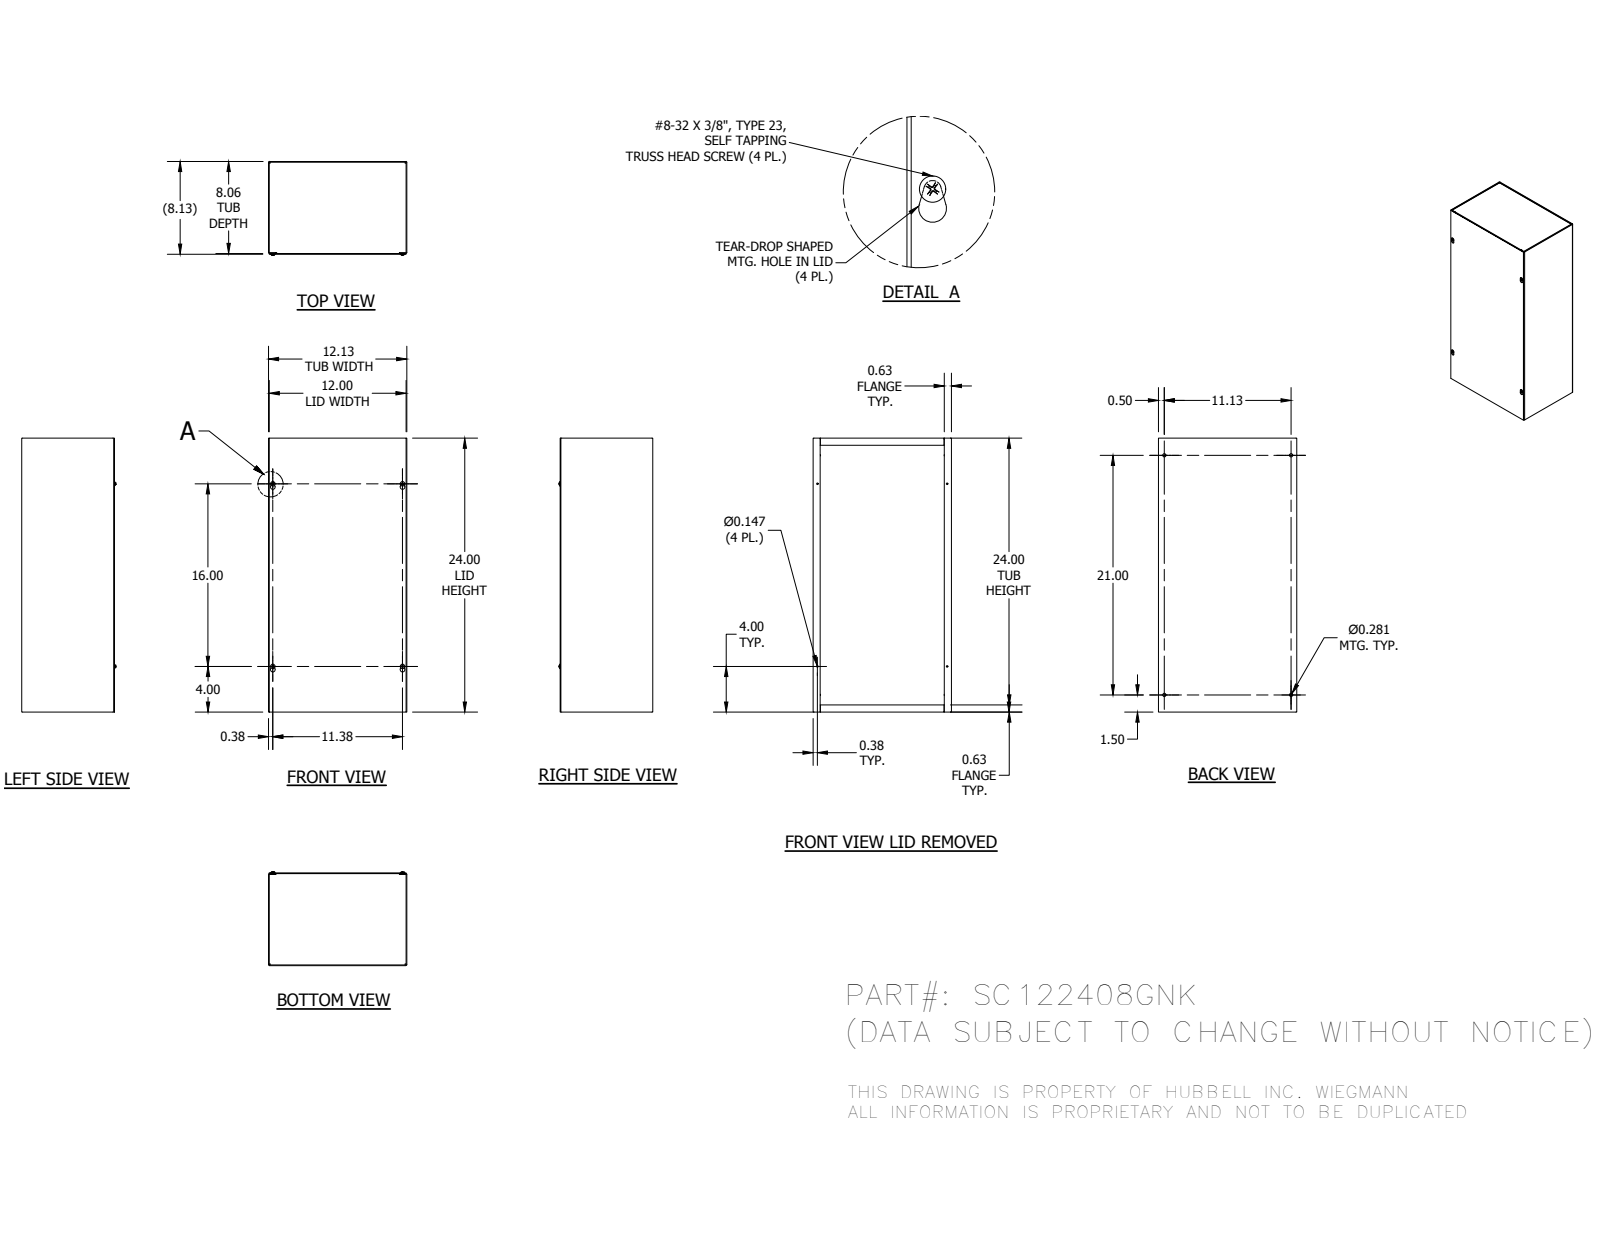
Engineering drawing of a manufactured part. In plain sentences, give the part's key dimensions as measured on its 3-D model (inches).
The part is named "SC122408GNKBLR; SC1208GNKTB; SC1224GLPA; 34056 (+1 more)". Its 3-D file was written by "Autodesk Inventor 2014 (AUTOMOTIVE_DESIGN)". It is 8 solids with 268 faces: 152 planar, 48 cylindrical and 68 other. Overall it measures 24 by 12.125 by 8.225 inches. Its volume is 76.34 cubic inches and its surface area 2 460 square inches. Round holes: 4 of diameter 0.147, 4 of diameter 0.281. Round bosses or shafts: 4 of diameter 0.384, 4 of diameter 0.164. Partial cylindrical surfaces (rounded edges, fillets, slot ends): 12 of radius 0.016, 12 of radius 0.078, 4 of radius 0.125, 4 of radius 0.203. The main face-to-face distances are 0.063, 12.063, 8, 0.062, 8.063, 8.062, 8.125, 12, 12.125, 23.937. The hole center spacings are 2.503, 11.524, 18.5, 21.652, 11.125, 11.375, 16, 19.631.
